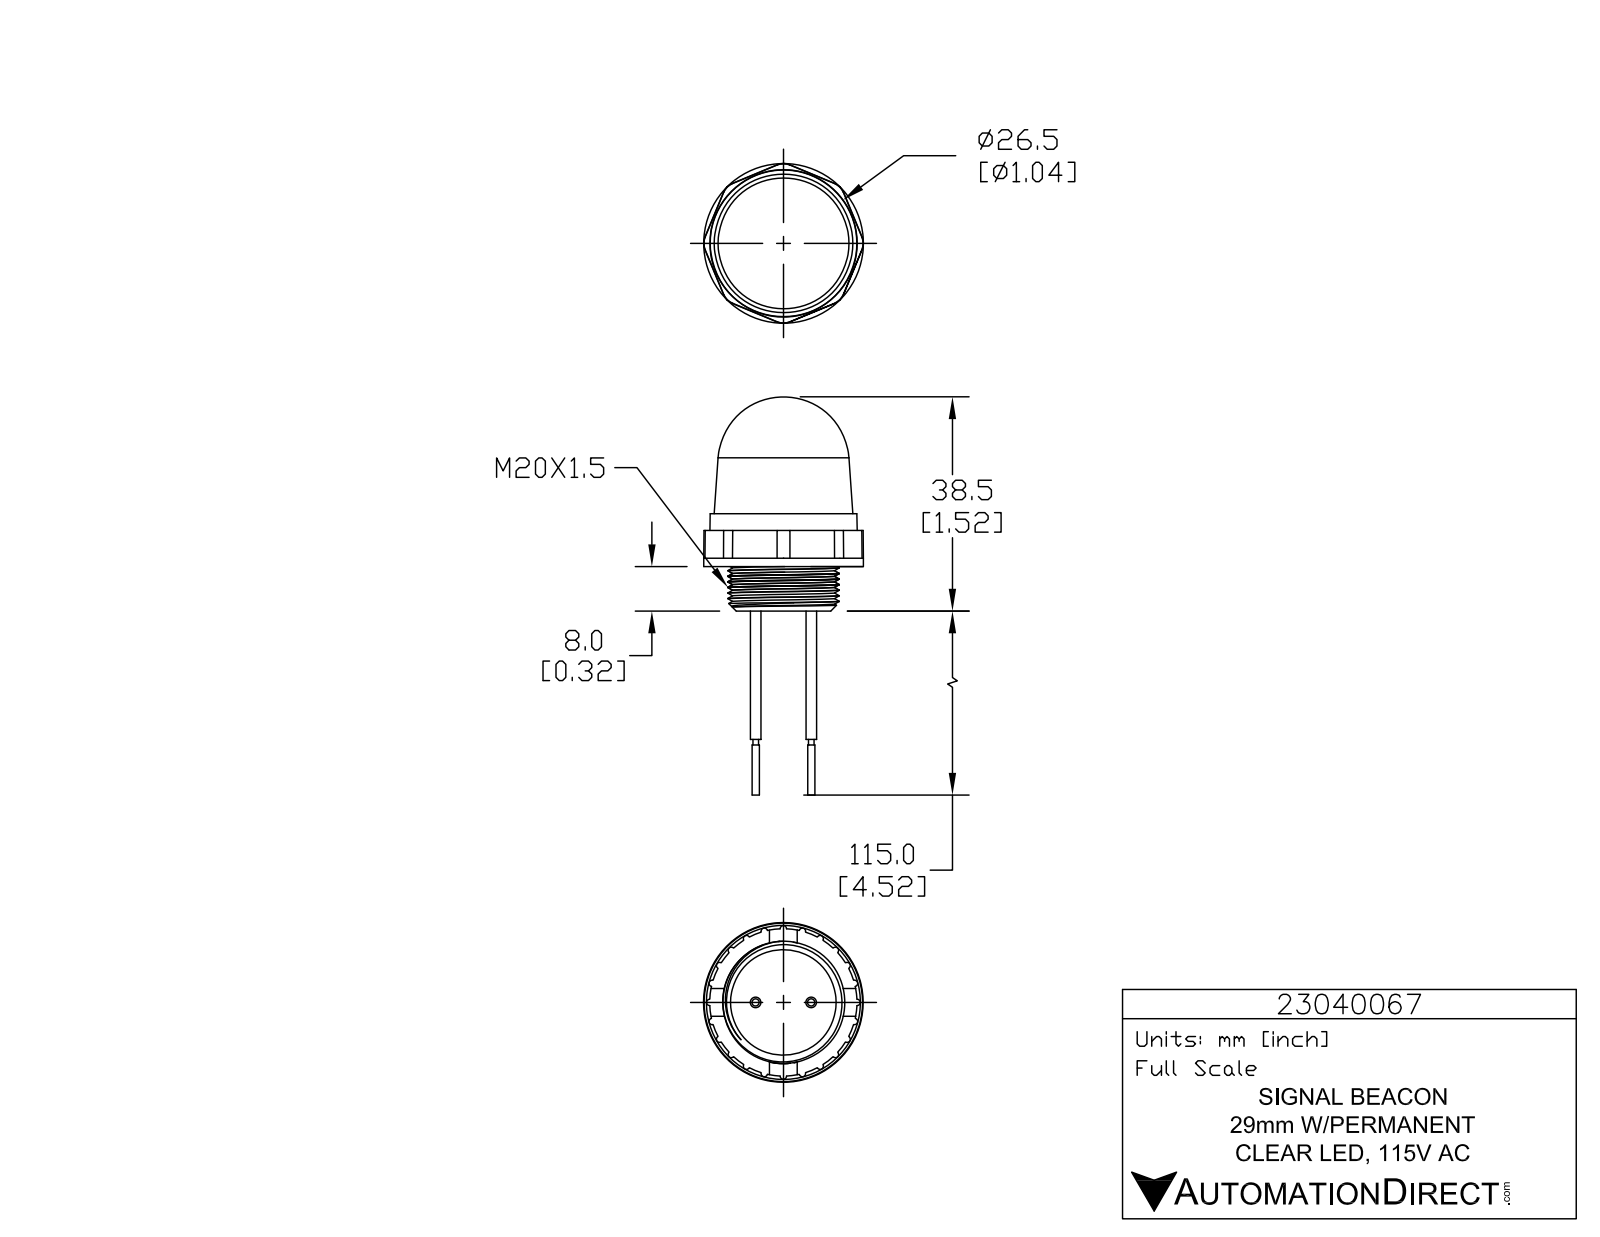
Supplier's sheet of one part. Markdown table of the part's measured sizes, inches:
| quantity | value |
| --- | --- |
| part name | 23040067 |
| STEP written by | SolidWorks 2017 (AUTOMOTIVE_DESIGN) |
| units | inches |
| bodies | 1 solid, 844 faces (551 planar, 203 cylindrical, 90 other) |
| overall size | 2.82 × 1.131 × 1.131 |
| volume | 0.978 in³ |
| surface area | 8.158 in² |
| round holes (diameter × count) | 0.02 × 3, 0.807 × 1 |
| round bosses / shafts (diameter × count) | 0.113 × 3, 0.028 × 3, 0.075 × 2, 0.051 × 2, 0.039 × 2, 1.131 × 1, 1.122 × 1, 0.894 × 1 |
| partial cylindrical surfaces (radius × count) | 0.118 × 8, 0.004 × 6, 0.004 × 6, 0.004 × 6, 0.065 × 6, 0.005 × 3, 0.007 × 3, 0.008 × 3 |
| main face-to-face distances | 0.276, 0.374, 0.039, 0.315, 0.65, 0.638, 0.362, 0.689, 0.413, 0.051 |
